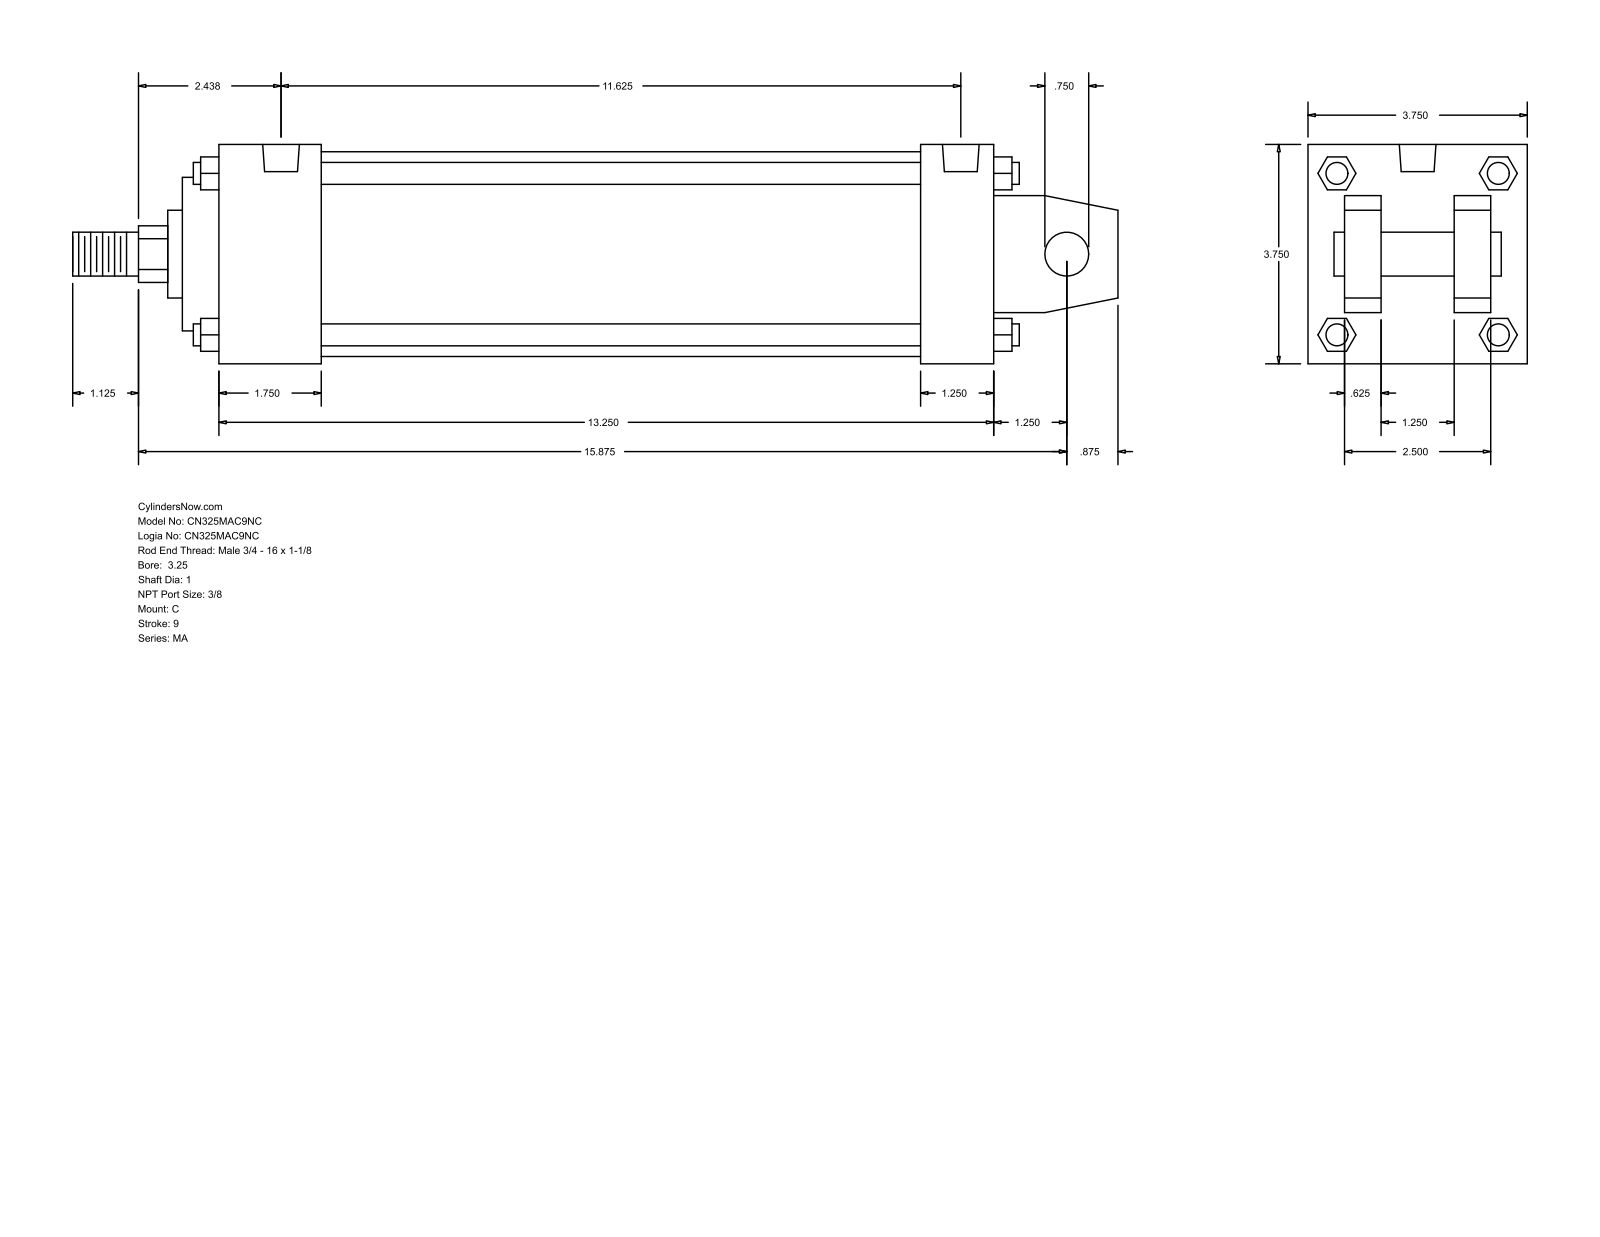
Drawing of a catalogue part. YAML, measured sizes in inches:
part_name: "MA_C__0325_1"
step_written_by: "GSSL Pune (CONFIG_CONTROL_DESIGN)"
units: inches
bodies: {solids: 0, faces: 141, planar: 109, cylindrical: 32, other: 0}
overall_size: [17.875, 3.75, 3.75]
round_holes:
  - {diameter: 0.437, count: 4}
  - {diameter: 0.627, count: 2}
round_bosses_or_shafts:
  - {diameter: 0.375, count: 4}
  - {diameter: 0.75, count: 2}
  - {diameter: 3.5, count: 1}
  - {diameter: 2.625, count: 1}
  - {diameter: 1.5, count: 1}
  - {diameter: 1, count: 1}
partial_cylinders:
  - {radius: 0.484, count: 1}
face_to_face_distances: [3.75, 0.625, 2.5, 13.25, 1.25, 3.125, 1.875, 12, 1.25, 1.75]
hole_center_spacings: [0.187, 11.25, 11.438, 11.625]
